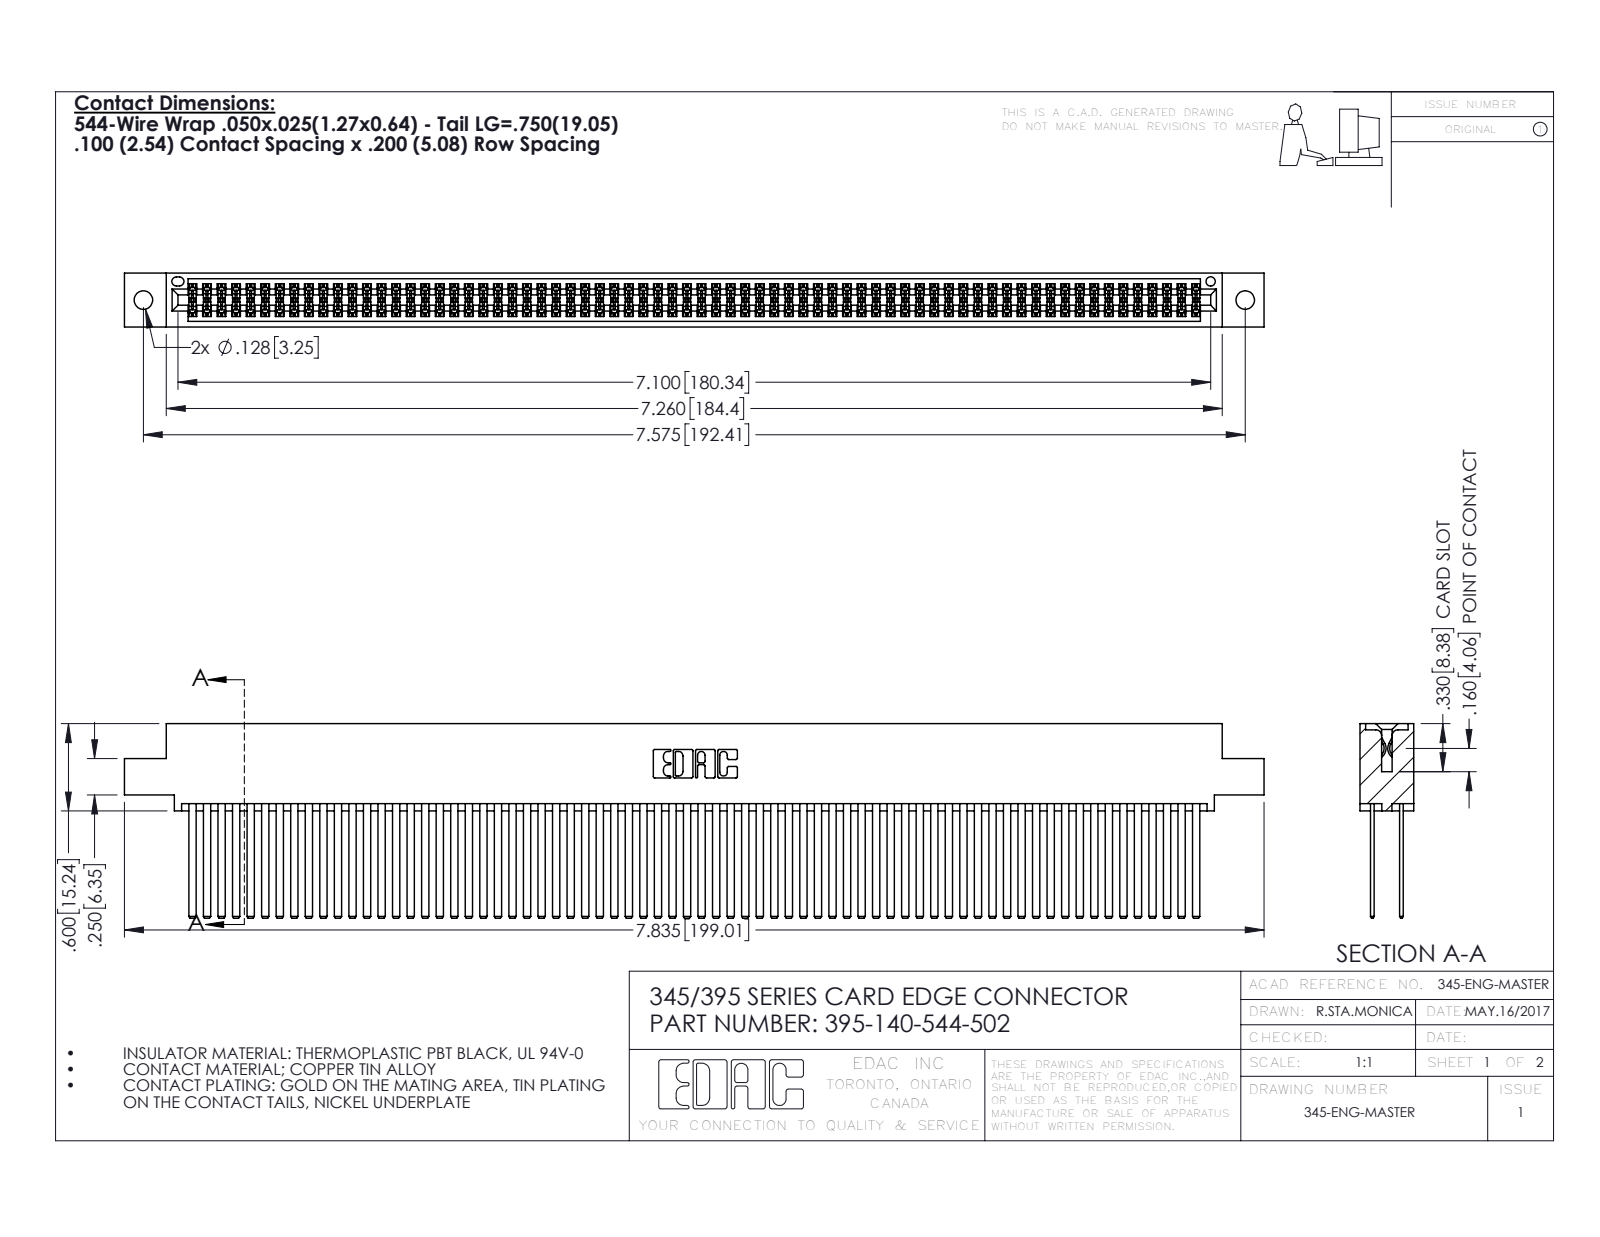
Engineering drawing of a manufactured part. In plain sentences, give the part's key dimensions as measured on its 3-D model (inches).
The part is named "345 Part_0.110 Offset - 0.128 Dia; 345-292-001_345-293-144; 395-140-544-502". Its 3-D file was written by "SolidWorks 2016 (CONFIG_CONTROL_DESIGN)". It is 141 solids with 6290 faces: 4144 planar, 2146 cylindrical and 0 other. Overall it measures 7.835 by 1.337 by 0.37 inches. Its volume is 1.309 cubic inches and its surface area 58.61 square inches. Round holes: 2 of diameter 0.128, 1 of diameter 0.064. Partial cylindrical surfaces (rounded edges, fillets, slot ends): 210 of radius 0.006, 22 of radius 0.01, 6 of radius 0.007, 6 of radius 0.031, 3 of radius 0.026, 2 of radius 0.014, 2 of radius 0.019, 2 of radius 0.022. The main face-to-face distances are 0.2, 0.025, 0.298, 0.072, 0.098, 0.272, 0.225, 0.175, 0.37, 0.149. The hole center spacings are 0.27, 7.339, 7.575.
